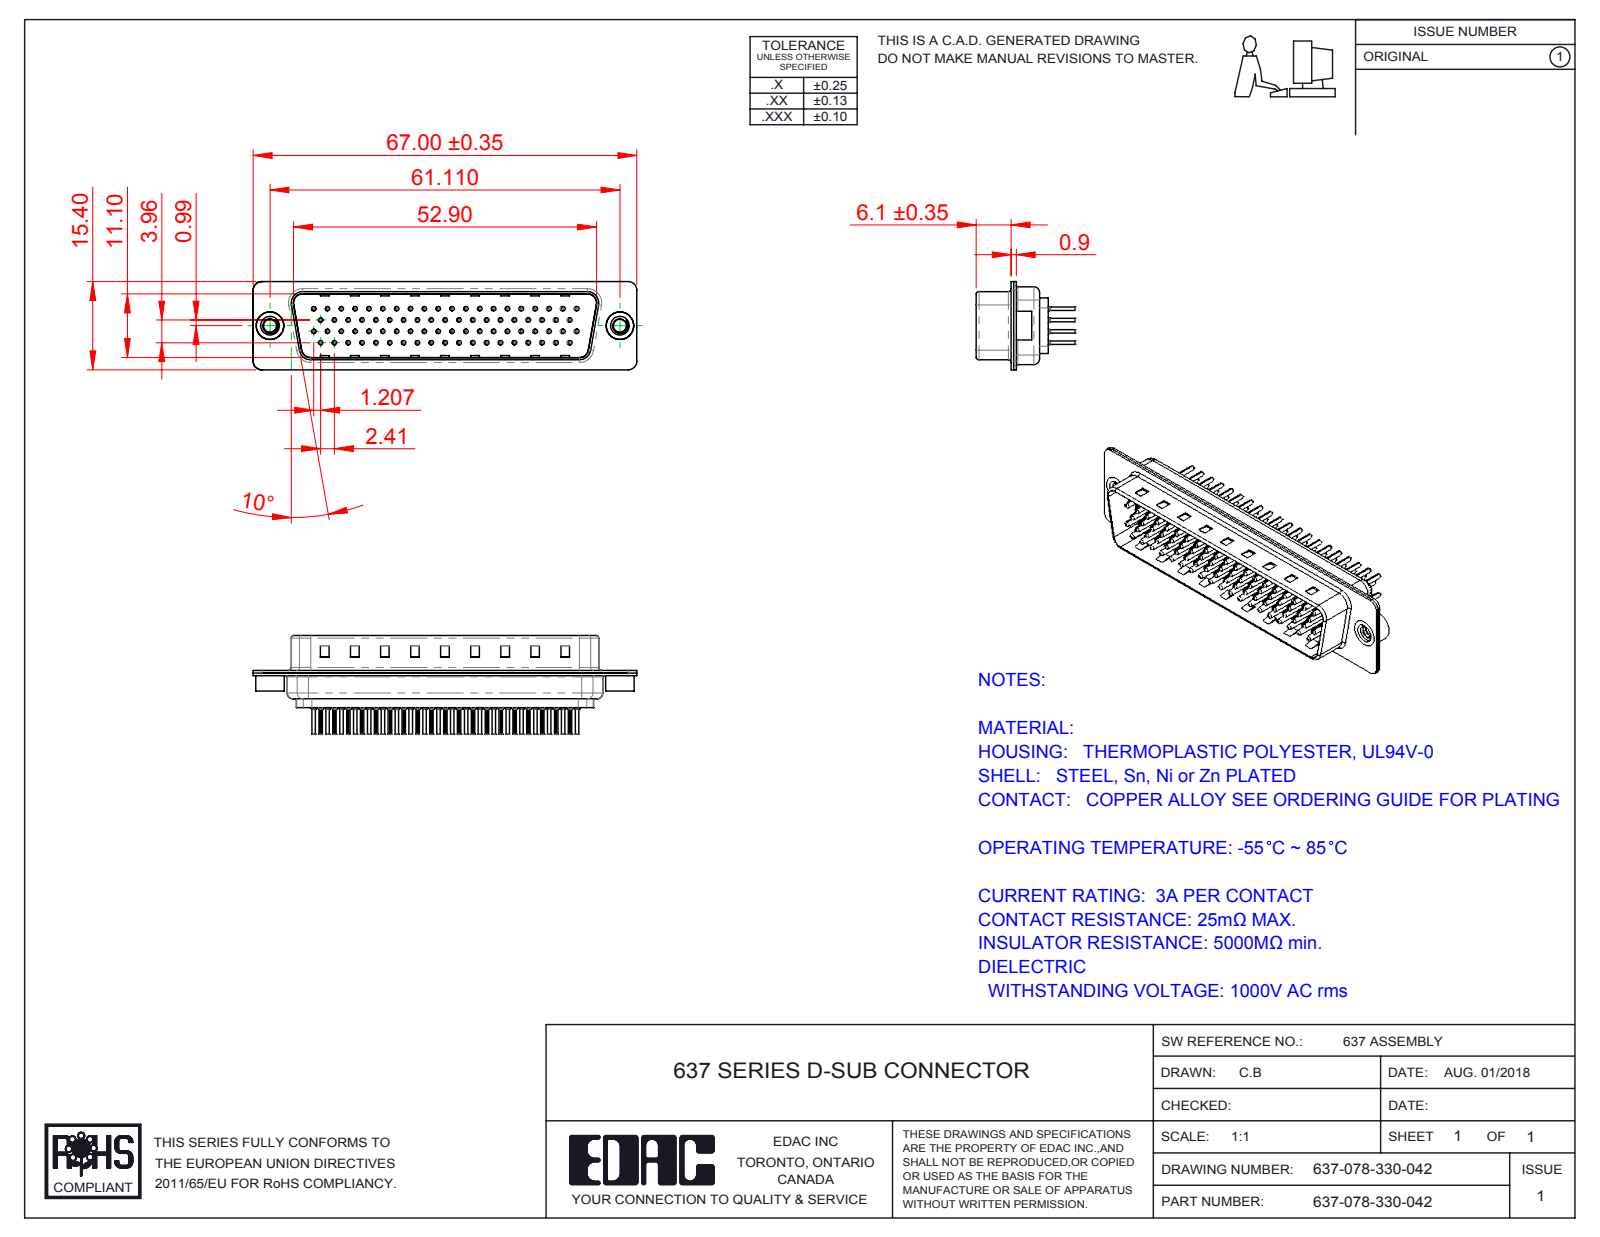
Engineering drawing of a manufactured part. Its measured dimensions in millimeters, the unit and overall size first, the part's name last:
Units: millimetres
Overall size (bounding box): 67 × 17.25 × 15.4
Round holes (diameter × count): ⌀1.6 ×150, ⌀0.2 ×78, ⌀0.35 ×78, ⌀1.1 ×78, ⌀0.75 ×72, ⌀2 ×72, ⌀4 ×3, ⌀2.26 ×2, ⌀4.8 ×2
Round bosses / shafts (diameter × count): ⌀2 ×78, ⌀1.5 ×78, ⌀0.75 ×78, ⌀0.6 ×78, ⌀5 ×2, ⌀4.9 ×2, ⌀4.8 ×1
Partial cylindrical surfaces — rounded edges, fillets, slot ends (radius × count): R0.1 ×156, R1.5 ×16, R2 ×12, R0.5 ×8, R0.25 ×4, R0.55 ×4, R0.7 ×4, R0.95 ×4
Main face-to-face distances: 0.45, 0.4, 1.5, 1.95, 11.9, 11.5, 0.7, 11.1, 0.9, 0.8
Hole centre spacings: 2.41, 7.24, 6.06, 9.65, 6.96, 8.46, 14.54, 16.89
Volume: 4 336 mm³ · Surface area: 15 865 mm²
Bodies: 83 solids, 8212 faces (2075 planar, 3027 cylindrical, 3110 other)
Part name (STEP PRODUCT): 637 Shell Front_78 Contacts; 637-078-330-042; 637 Contact Row 3_30; 637 Contact Row 2_30 (+5 more)
STEP written by: SolidWorks 2016 (CONFIG_CONTROL_DESIGN)
